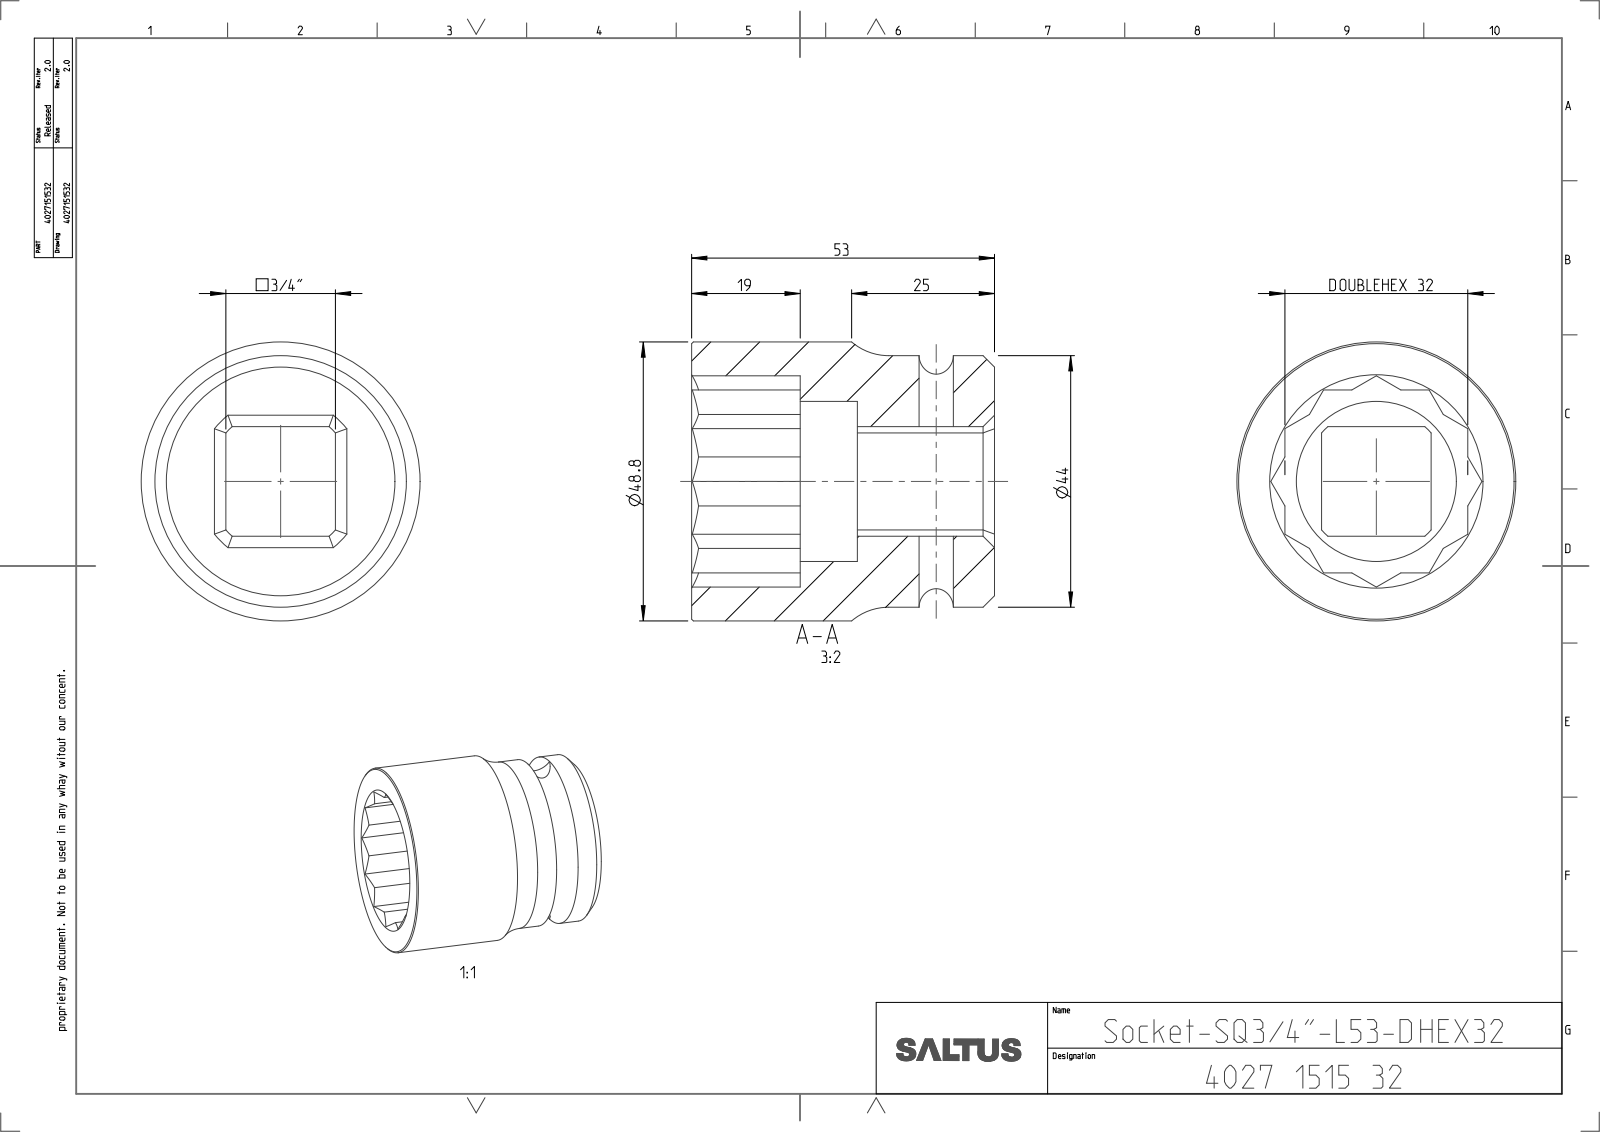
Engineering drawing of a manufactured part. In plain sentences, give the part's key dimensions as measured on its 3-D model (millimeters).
The part is named "4027151532". Its 3-D file was written by "CREO PARAMETRIC BY PTC INC, 2022414 (CONFIG_CONTROL_DESIGN)". It is 1 solid with 66 faces: 36 planar, 16 cylindrical and 14 other. Overall it measures 53 by 48.8 by 48.8 millimeters. Its volume is 55 216 cubic millimeters and its surface area 15 725 square millimeters. Round holes: 1 of diameter 6, 1 of diameter 28. Round bosses or shafts: 1 of diameter 48.8, 1 of diameter 44. Partial cylindrical surfaces (rounded edges, fillets, slot ends): 1 of radius 12.8. The main face-to-face distances are 32, 53, 6.41, 25.59, 19.18, 34, 19, 24, 10, 29.
